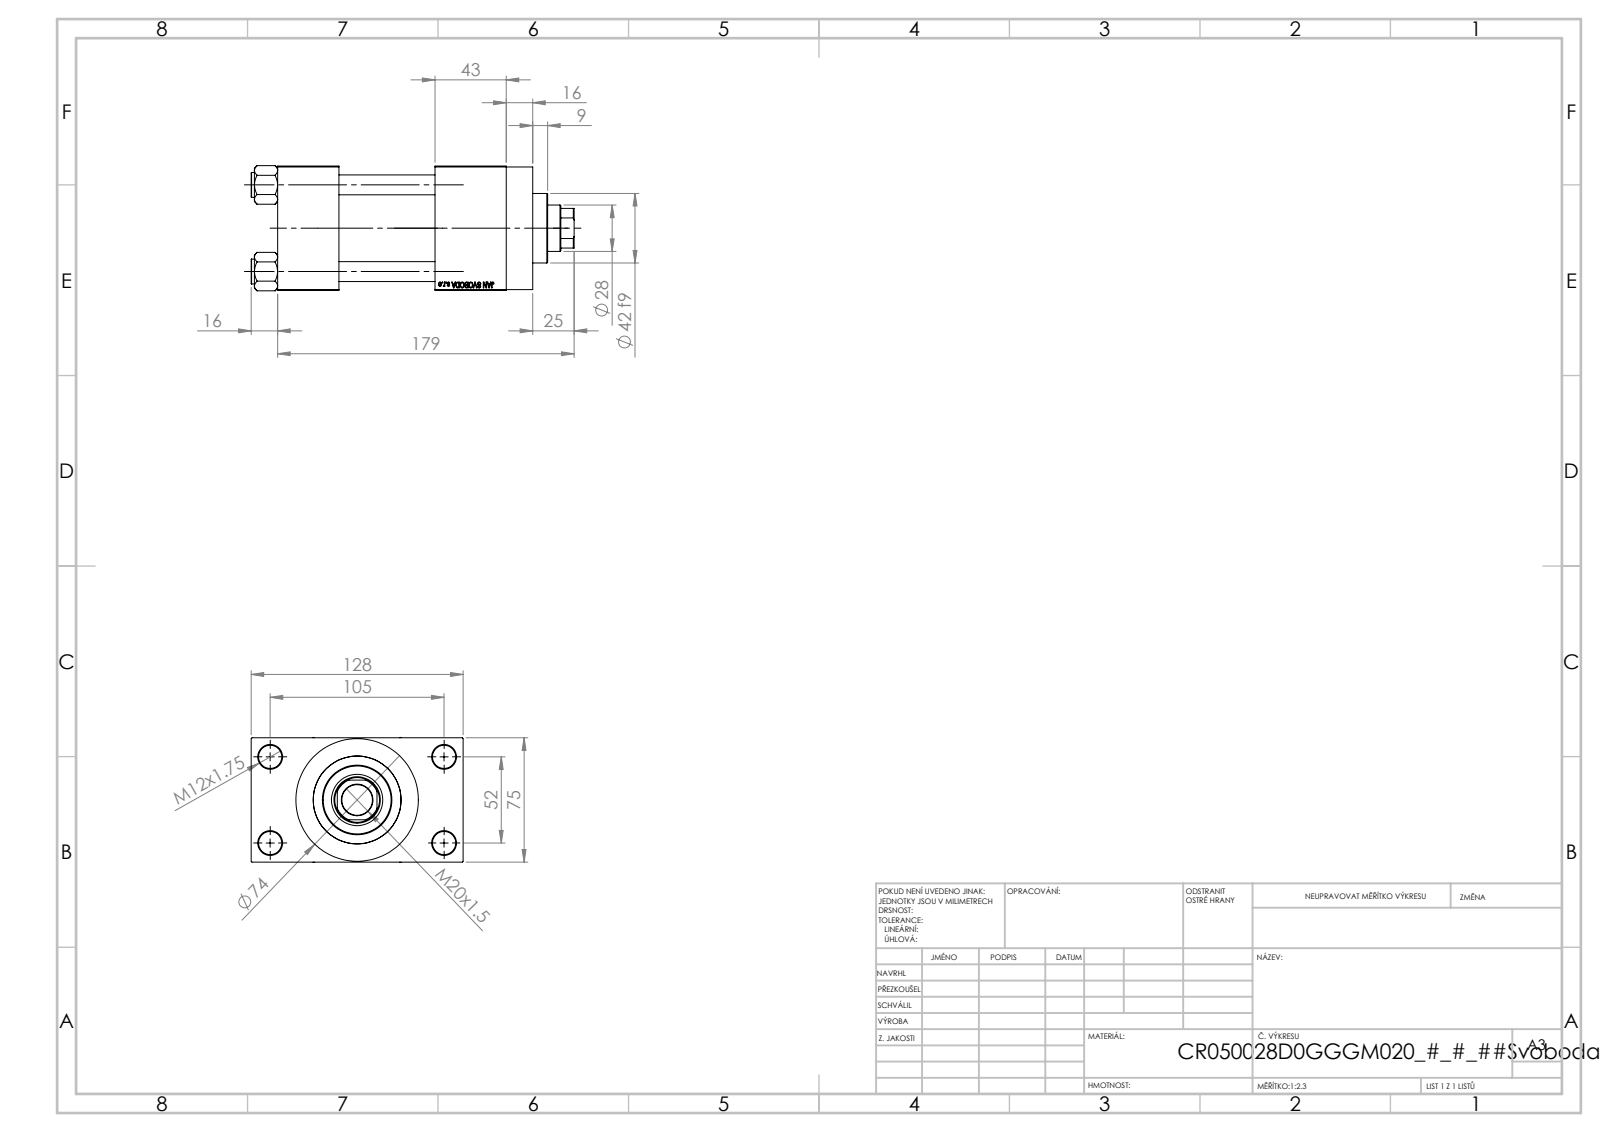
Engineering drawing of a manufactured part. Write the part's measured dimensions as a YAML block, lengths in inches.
part_name: "V215CR_D_Body; NUT_M5_D; V215CR_D_TYCINKA; V215CR_VCP_D (+1 more)"
step_written_by: "SolidWorks 2019 (CONFIG_CONTROL_DESIGN)"
units: inches
bodies: {solids: 11, faces: 1104, planar: 497, cylindrical: 89, other: 518}
overall_size: [7.677, 5.039, 2.974]
volume: 49.75
surface_area: 261.7
round_holes:
  - {diameter: 0.472, count: 4}
  - {diameter: 0.551, count: 4}
  - {diameter: 0.276, count: 2}
  - {diameter: 0.825, count: 2}
  - {diameter: 1.181, count: 2}
  - {diameter: 0.728, count: 1}
  - {diameter: 1.102, count: 1}
  - {diameter: 1.22, count: 1}
  - {diameter: 1.614, count: 1}
  - {diameter: 1.969, count: 1}
  - {diameter: 2.087, count: 1}
round_bosses_or_shafts:
  - {diameter: 0.591, count: 4}
  - {diameter: 2.913, count: 1}
  - {diameter: 2.205, count: 1}
  - {diameter: 1.654, count: 1}
partial_cylinders:
  - {radius: 0.531, count: 1}
face_to_face_distances: [2.953, 2.283, 1.457, 3.74, 1.043, 3.996, 5.433, 3.976, 1.693, 0.63]
hole_center_spacings: [1.037, 1.456, 2.059, 2.3, 2.307, 3.096, 3.715, 2.047]
